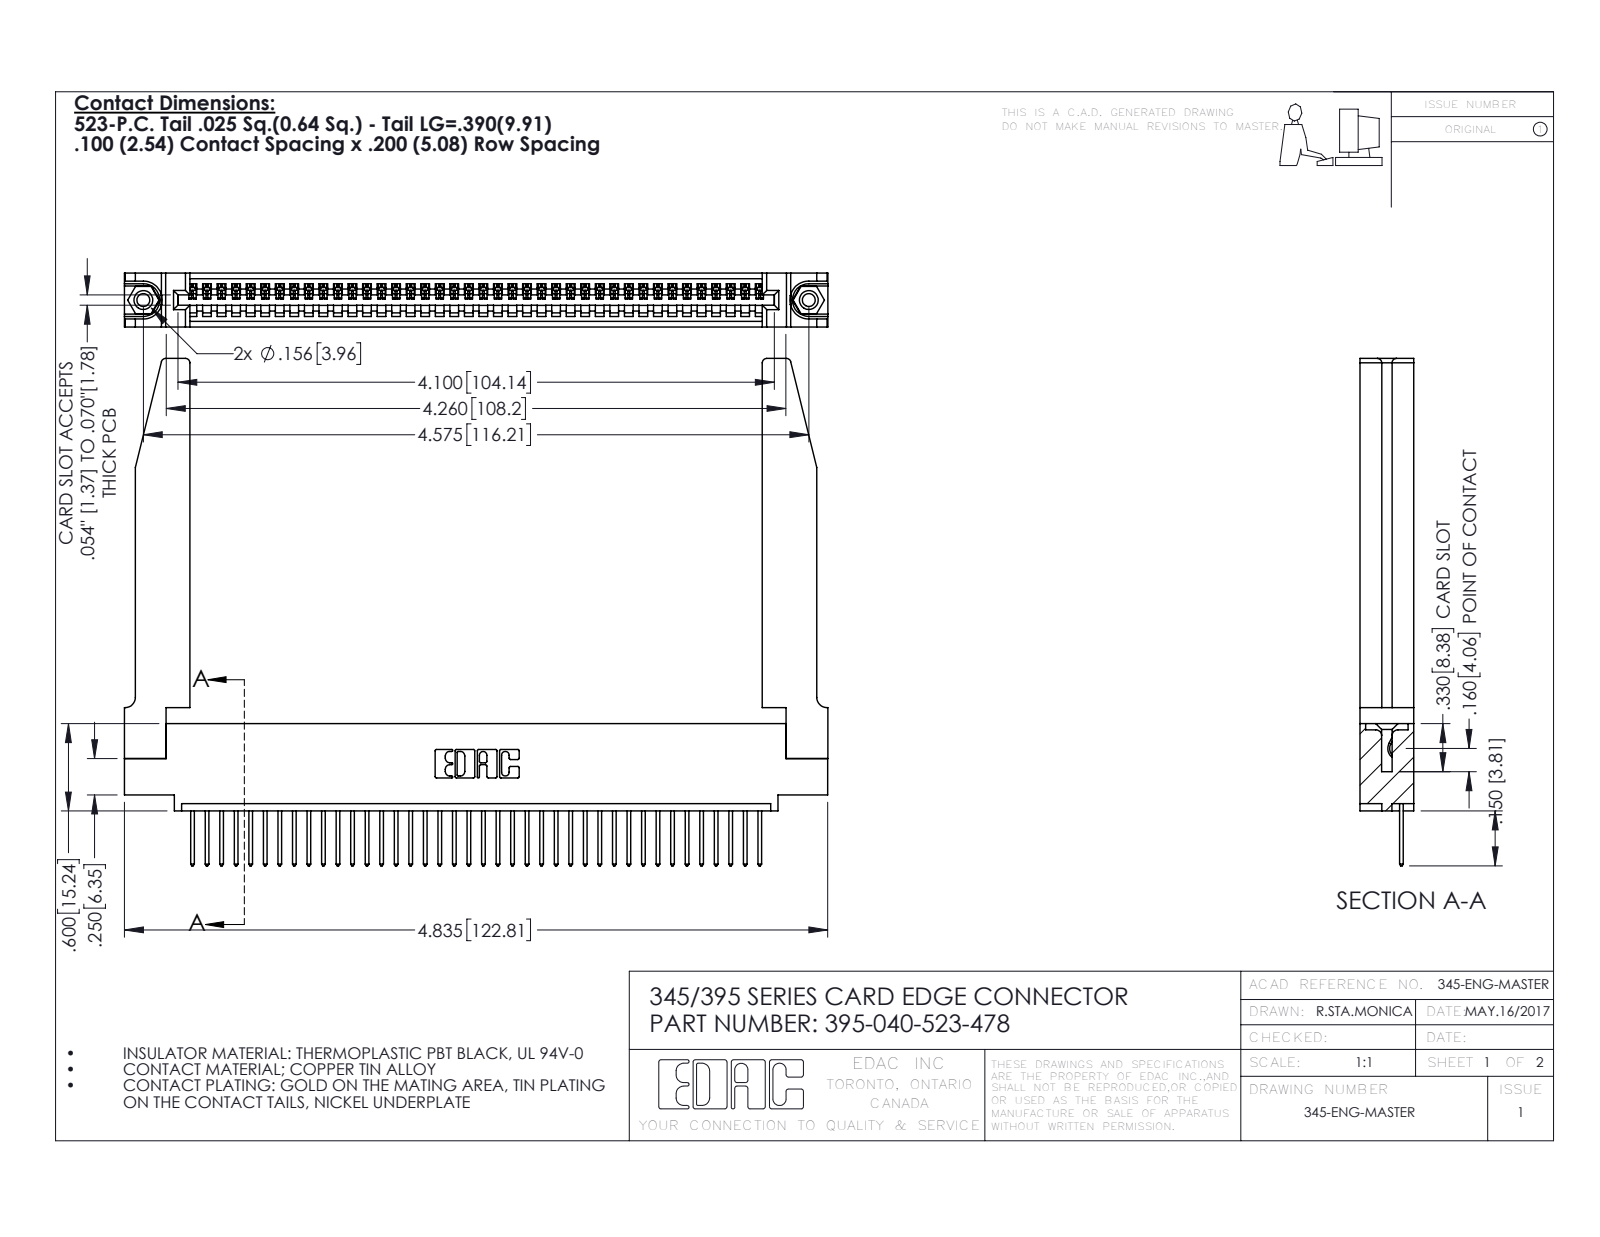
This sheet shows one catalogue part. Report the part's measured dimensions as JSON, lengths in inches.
{"part_name": "345-292-001_345-293-123; 345 Part_0.110 Offset - 0.156 Dia-TH; 395-040-523-478; 345-220-078_345-220-078 (+1 more)", "step_written_by": "SolidWorks 2016 (CONFIG_CONTROL_DESIGN)", "units": "inches", "bodies": {"solids": 45, "faces": 2684, "planar": 1826, "cylindrical": 806, "other": 52}, "overall_size": [4.836, 3.487, 0.37], "volume_in3": 1.18, "surface_area_in2": 34.58, "round_holes": [[0.089, 2], [0.125, 2], [0.156, 2], [0.064, 1]], "round_bosses_or_shafts": [[0.155, 2]], "partial_cylinders_radius": [[0.006, 80], [0.01, 80], [0.01, 22], [0.03, 8], [0.007, 6], [0.031, 6], [0.026, 3], [0.031, 2]], "face_to_face_distances": [0.37, 0.072, 0.298, 0.098, 0.272, 0.025, 0.2, 0.225, 0.148, 0.15], "hole_center_spacings": [0.27, 4.339, 4.575]}
